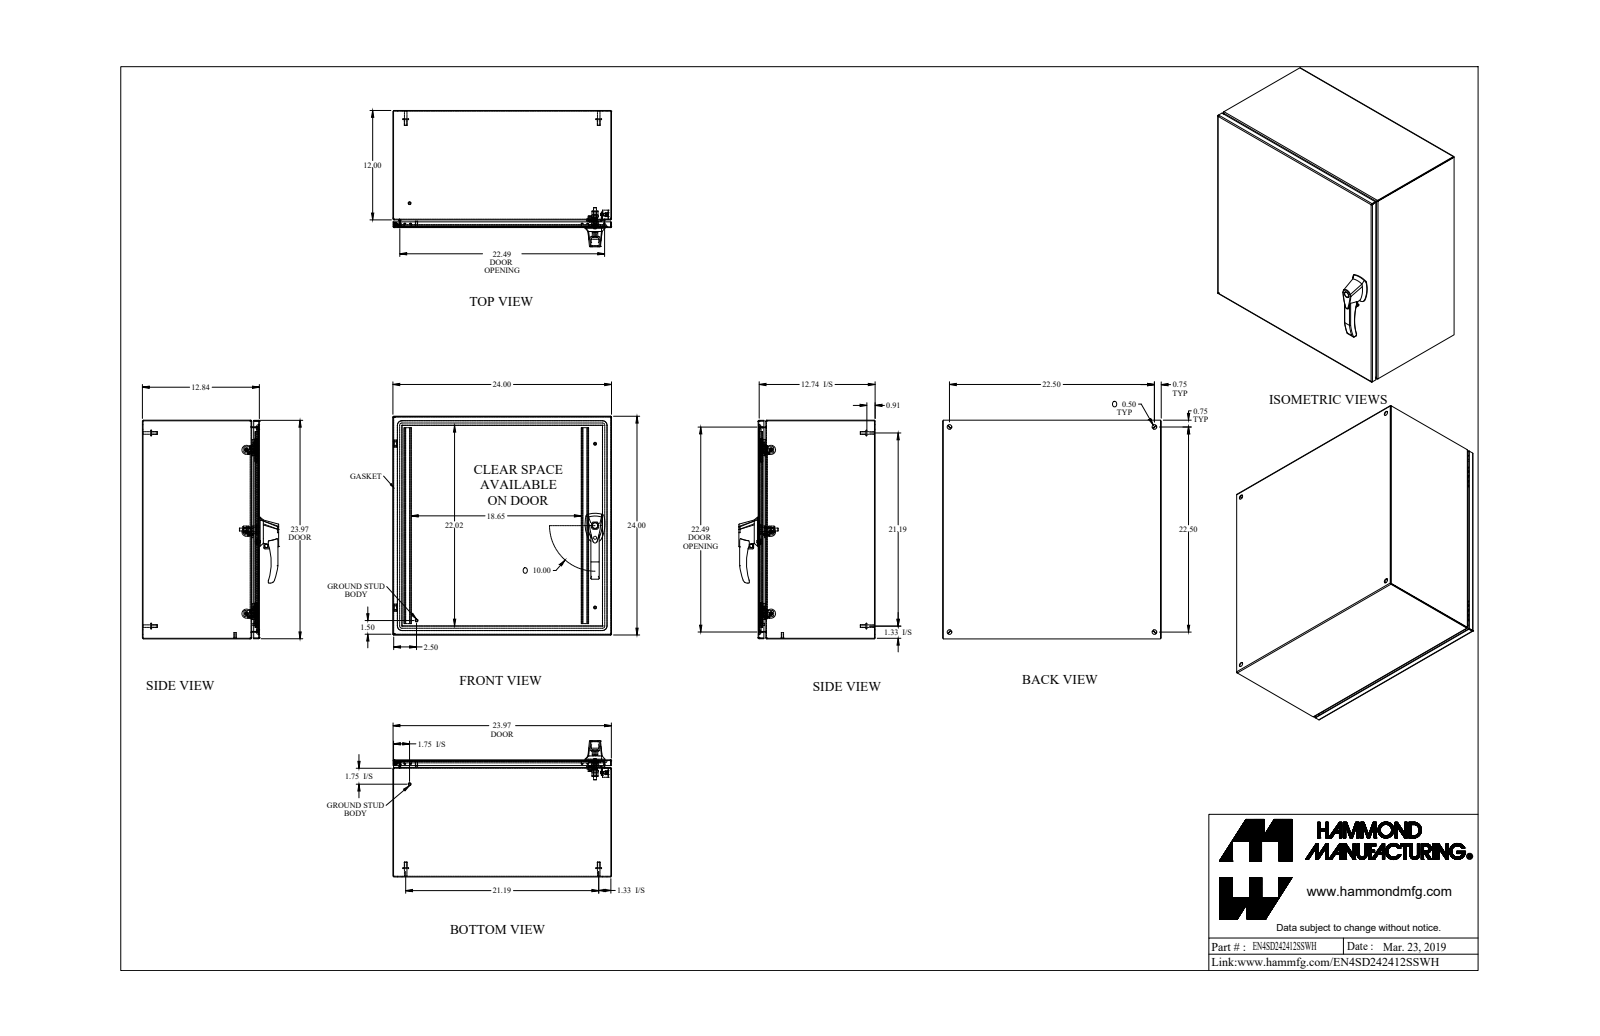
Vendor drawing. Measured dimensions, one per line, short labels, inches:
name: EN4SD242412SSWH
written by: SolidWorks 2019 (AUTOMOTIVE_DESIGN)
unit: in
bodies: 50 solids, 1218 faces (527 planar, 487 cylindrical, 204 other)
size: 24 × 24 × 14.958
volume: 205.3 in³; area: 5 461 in²
holes: 6× ⌀0.176, 4× ⌀0.5, 3× ⌀0.25, 3× ⌀0.265, 3× ⌀0.313, 3× ⌀0.413, 2× ⌀0.196, 2× ⌀0.256, 2× ⌀0.394, 1× ⌀0.172, 1× ⌀0.233, 1× ⌀0.24
bosses: 7× ⌀0.25, 6× ⌀0.375, 6× ⌀0.313, 6× ⌀0.156, 4× ⌀0.625, 4× ⌀0.275, 3× ⌀1, 3× ⌀0.51
rounds: 14× R0.036, 14× R0.108, 12× R0.01, 12× R0.048, 12× R0.312, 9× R0.125, 8× R0.1, 7× R0.06
face distances: 0.072, 12.771, 23.928, 12.699, 23.856, 12.843, 24, 0.843, 11.928, 23.178
hole spacings: 22.5, 0.786, 8.984, 8.985, 9, 17.969, 21.558, 24.211
